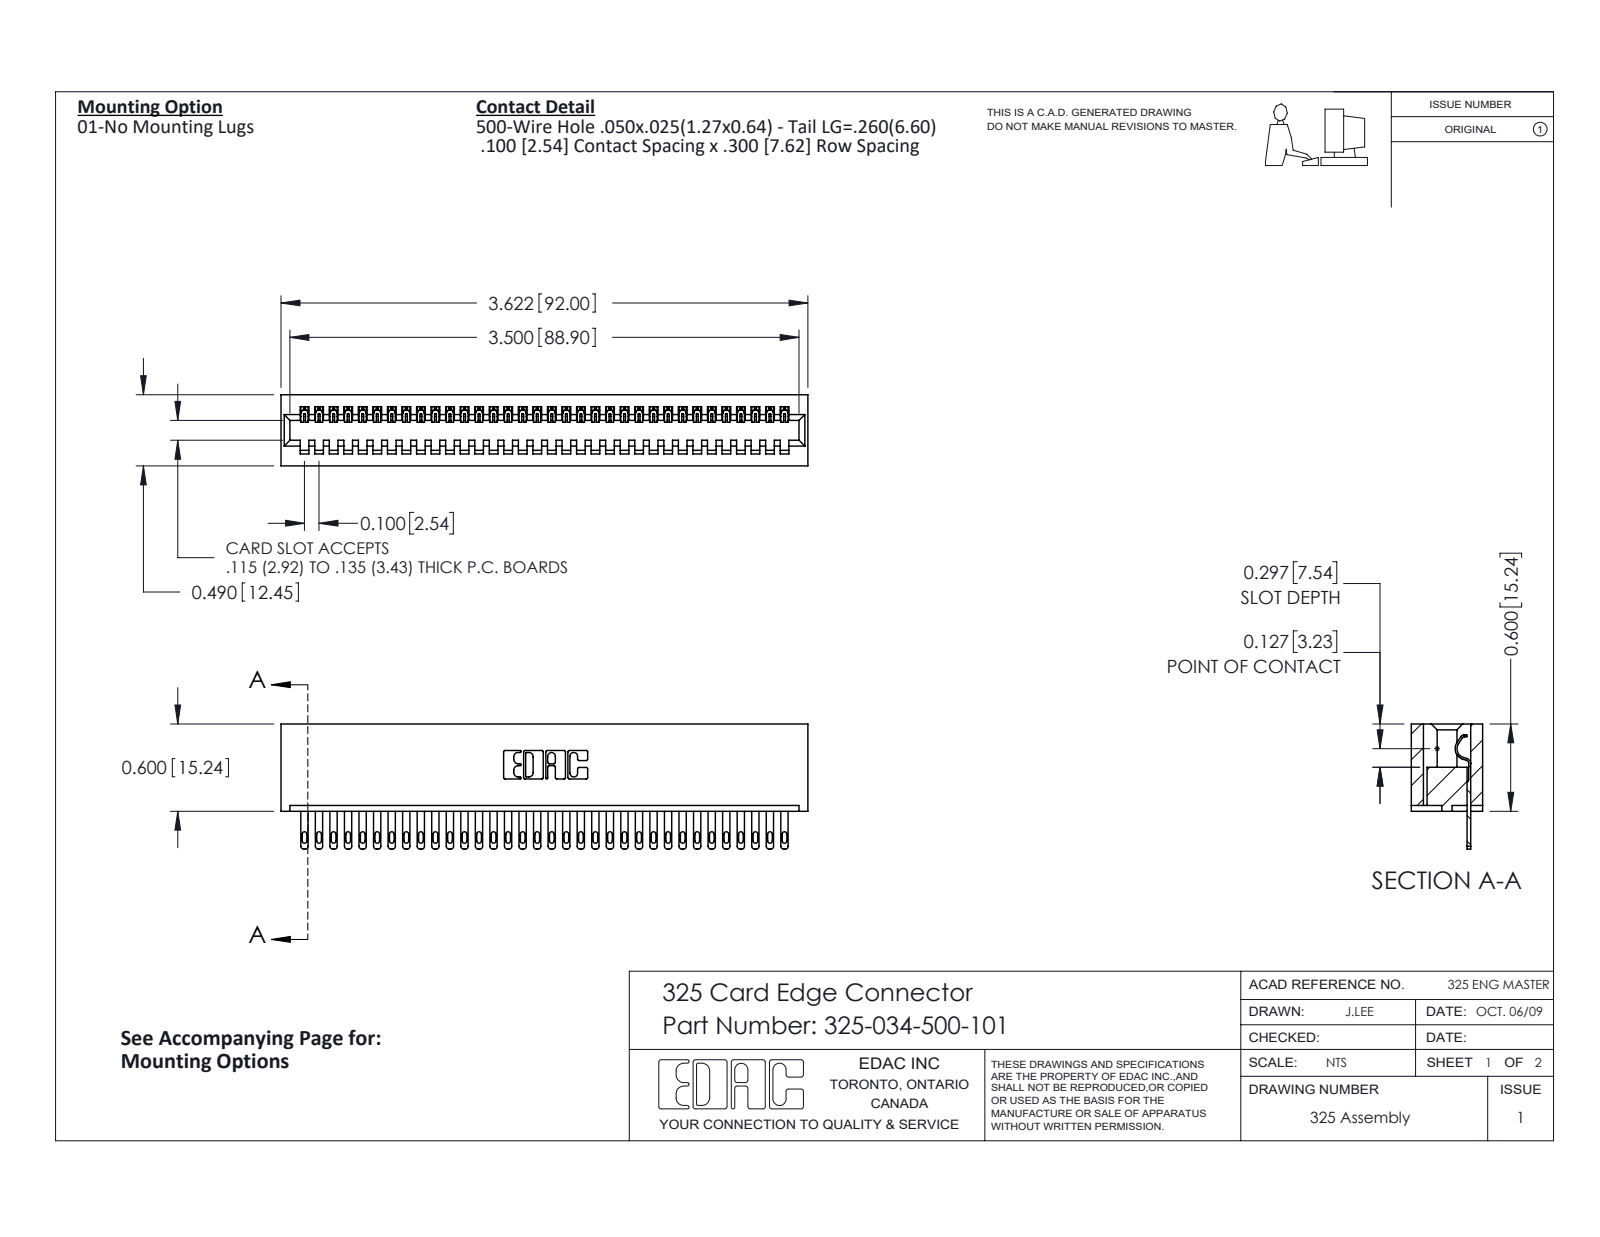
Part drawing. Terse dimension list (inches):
name: 325-034-500-101; 325-292-001_325-293-100; 325 Part_Lugless
written by: SolidWorks 2016 (CONFIG_CONTROL_DESIGN)
unit: in
bodies: 35 solids, 1942 faces (1290 planar, 652 cylindrical, 0 other)
size: 3.622 × 0.86 × 0.49
volume: 0.745 in³; area: 21.35 in²
rounds: 68× R0.006, 68× R0.016, 68× R0.02, 22× R0.01, 6× R0.007, 6× R0.031, 3× R0.026, 1× R0.014
face distances: 0.083, 0.407, 0.3, 0.49, 0.107, 0.383, 0.025, 0.325, 0.1, 0.56
